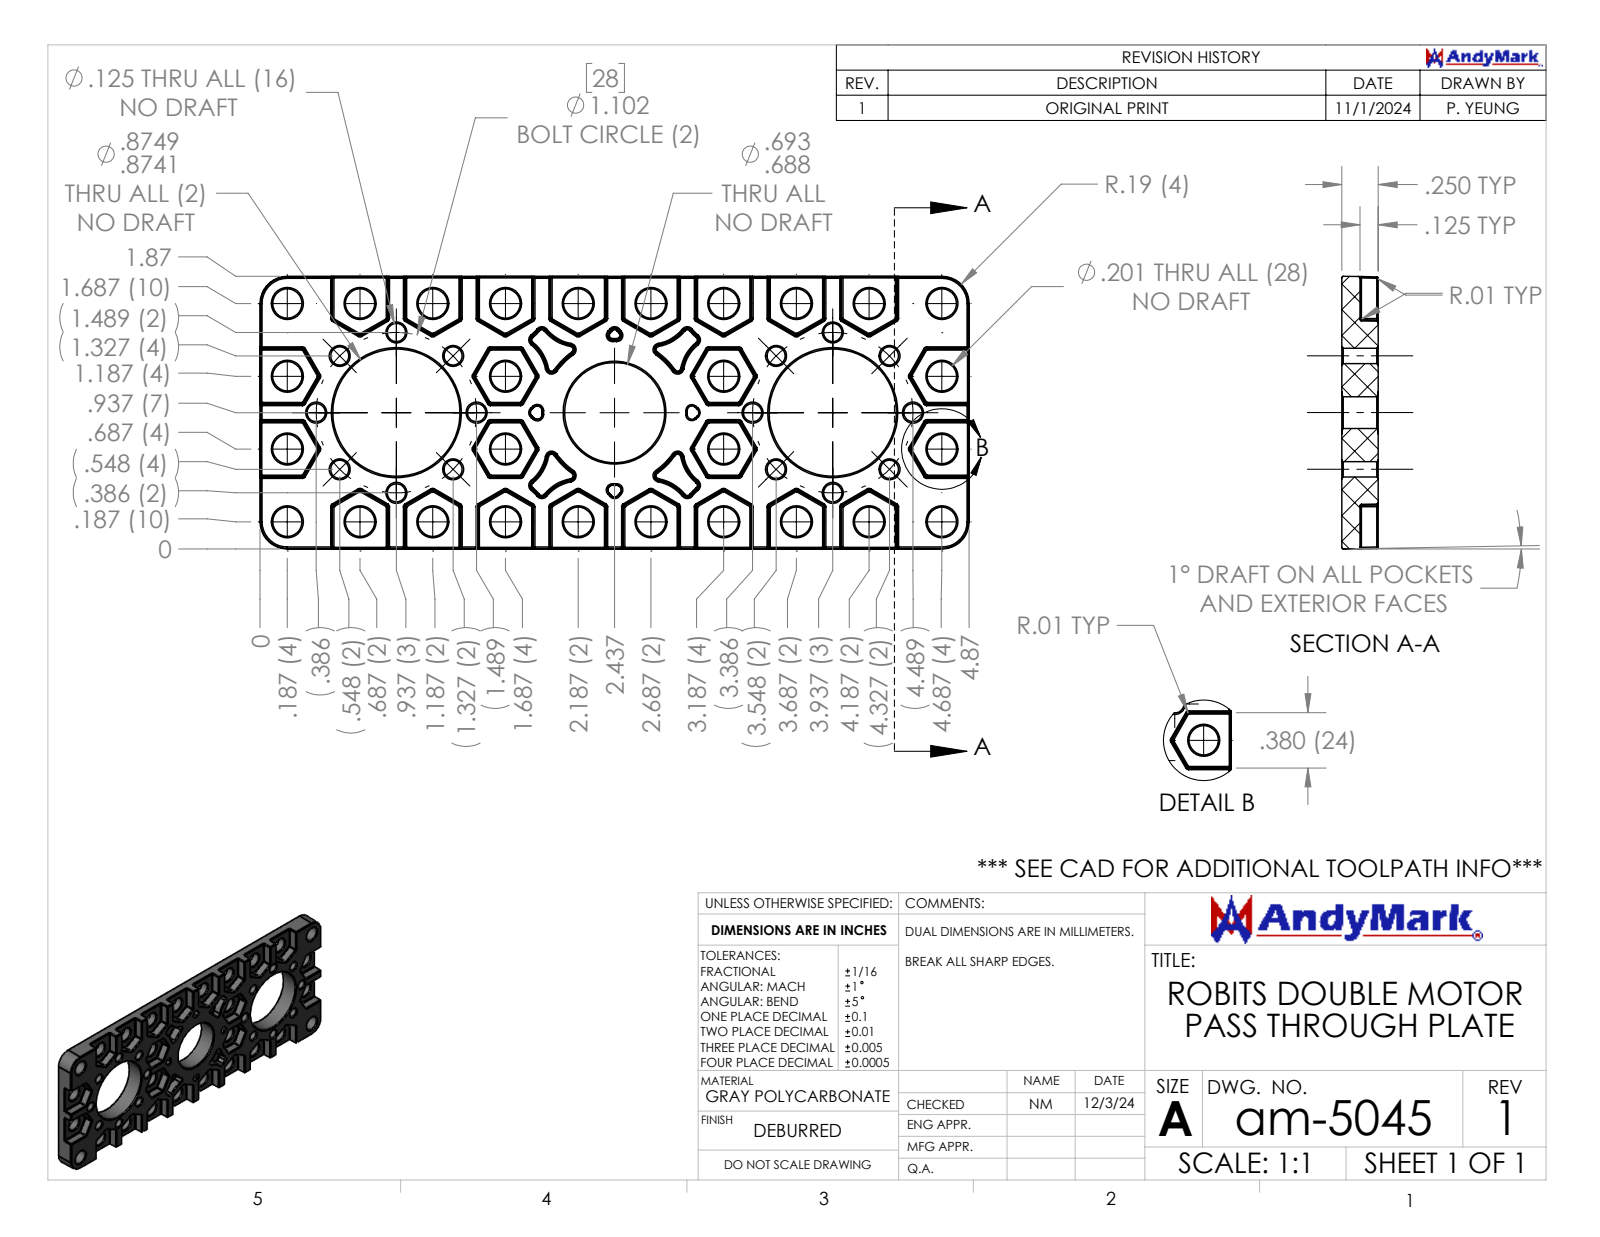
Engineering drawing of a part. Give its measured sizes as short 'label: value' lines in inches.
name: am-5045 Robits Double Motor Pass Through Plate
written by: SolidWorks 2024 (AUTOMOTIVE_DESIGN)
unit: in
bodies: 1 solid, 1263 faces (142 planar, 398 cylindrical, 723 other)
size: 4.875 × 1.875 × 0.25
volume: 1.276 in³; area: 24.31 in²
holes: 28× ⌀0.201, 10× ⌀0.125, 6× ⌀0.125, 2× ⌀0.874, 1× ⌀0.687
rounds: 204× R0.01, 3× R0.031, 2× R0.291, 1× R0.5
face distances: 0.25, 0.125, 0.125, 0.5, 1, 1.5, 2, 0.75, 2.5, 1.375
hole spacings: 0.422, 0.551, 0.78, 1.019, 0.776, 1.195, 1.502, 3
